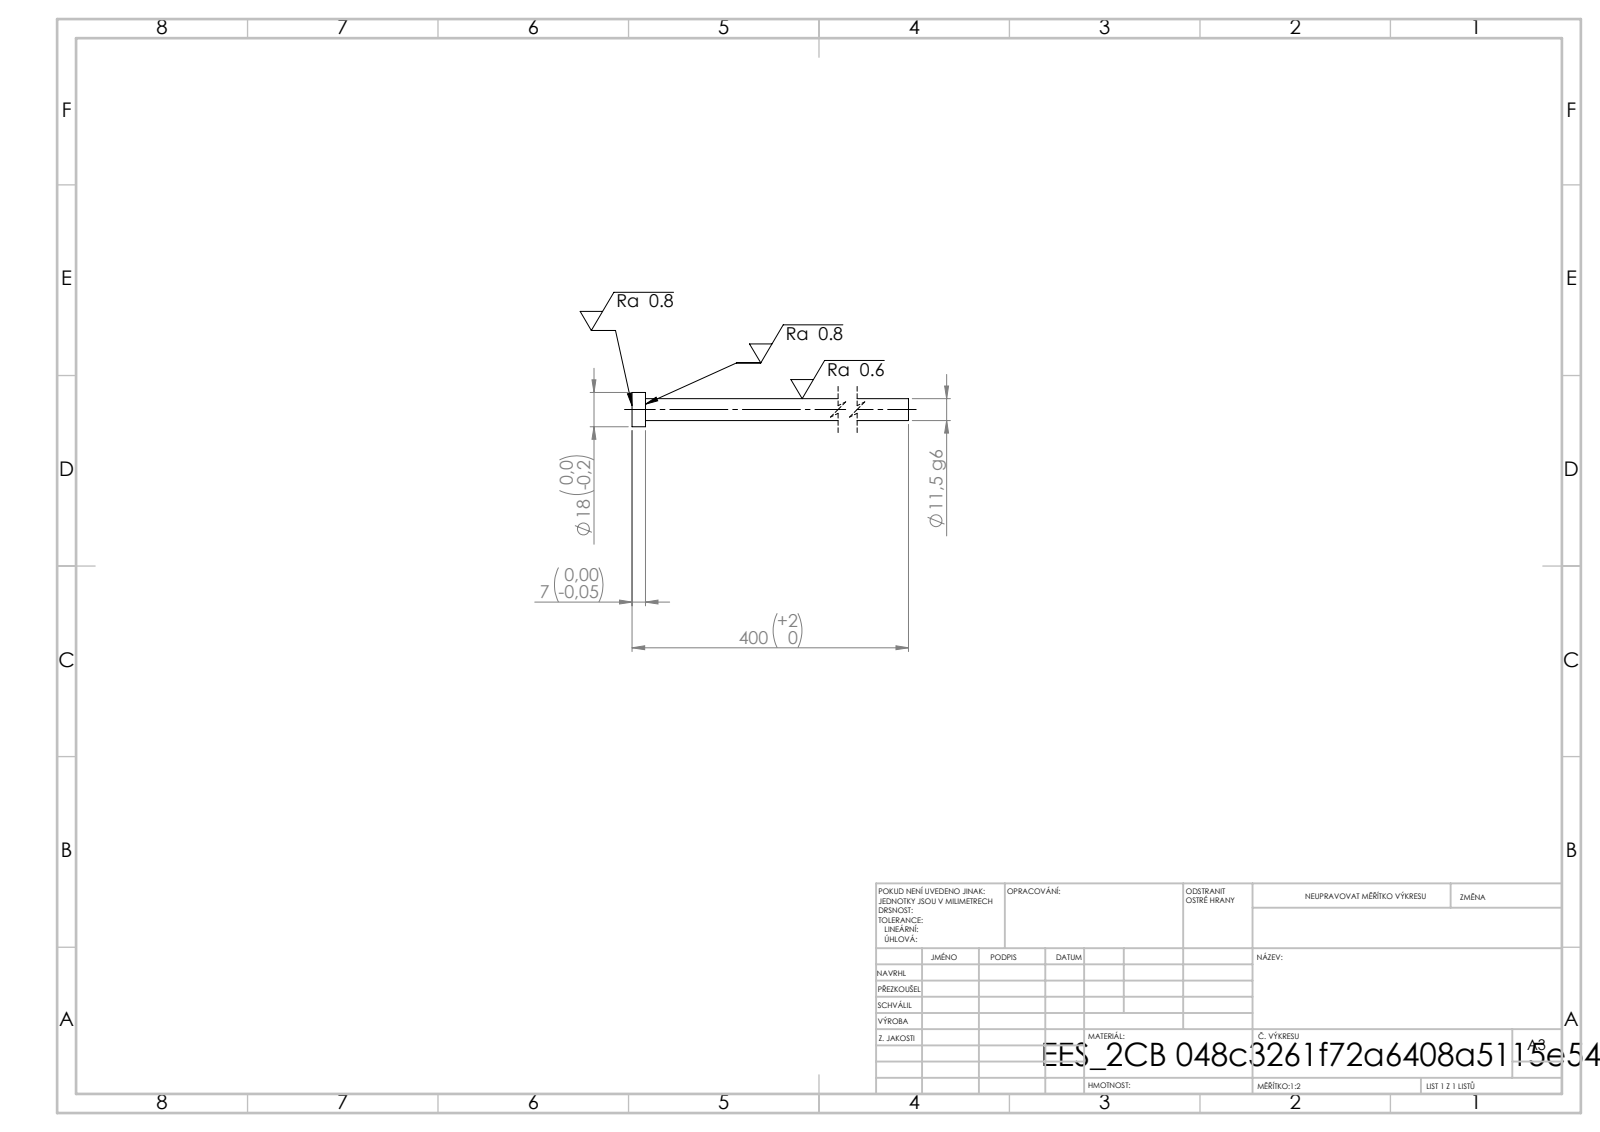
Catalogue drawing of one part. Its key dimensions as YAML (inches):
step_written_by: "SolidWorks 2019 (CONFIG_CONTROL_DESIGN)"
units: inches
bodies: {solids: 1, faces: 7, planar: 3, cylindrical: 4, other: 0}
overall_size: [15.748, 0.709, 0.709]
volume: 2.6
surface_area: 23.41
round_bosses_or_shafts:
  - {diameter: 0.709, count: 1}
  - {diameter: 0.453, count: 1}
face_to_face_distances: [0.276, 15.748, 15.472]
